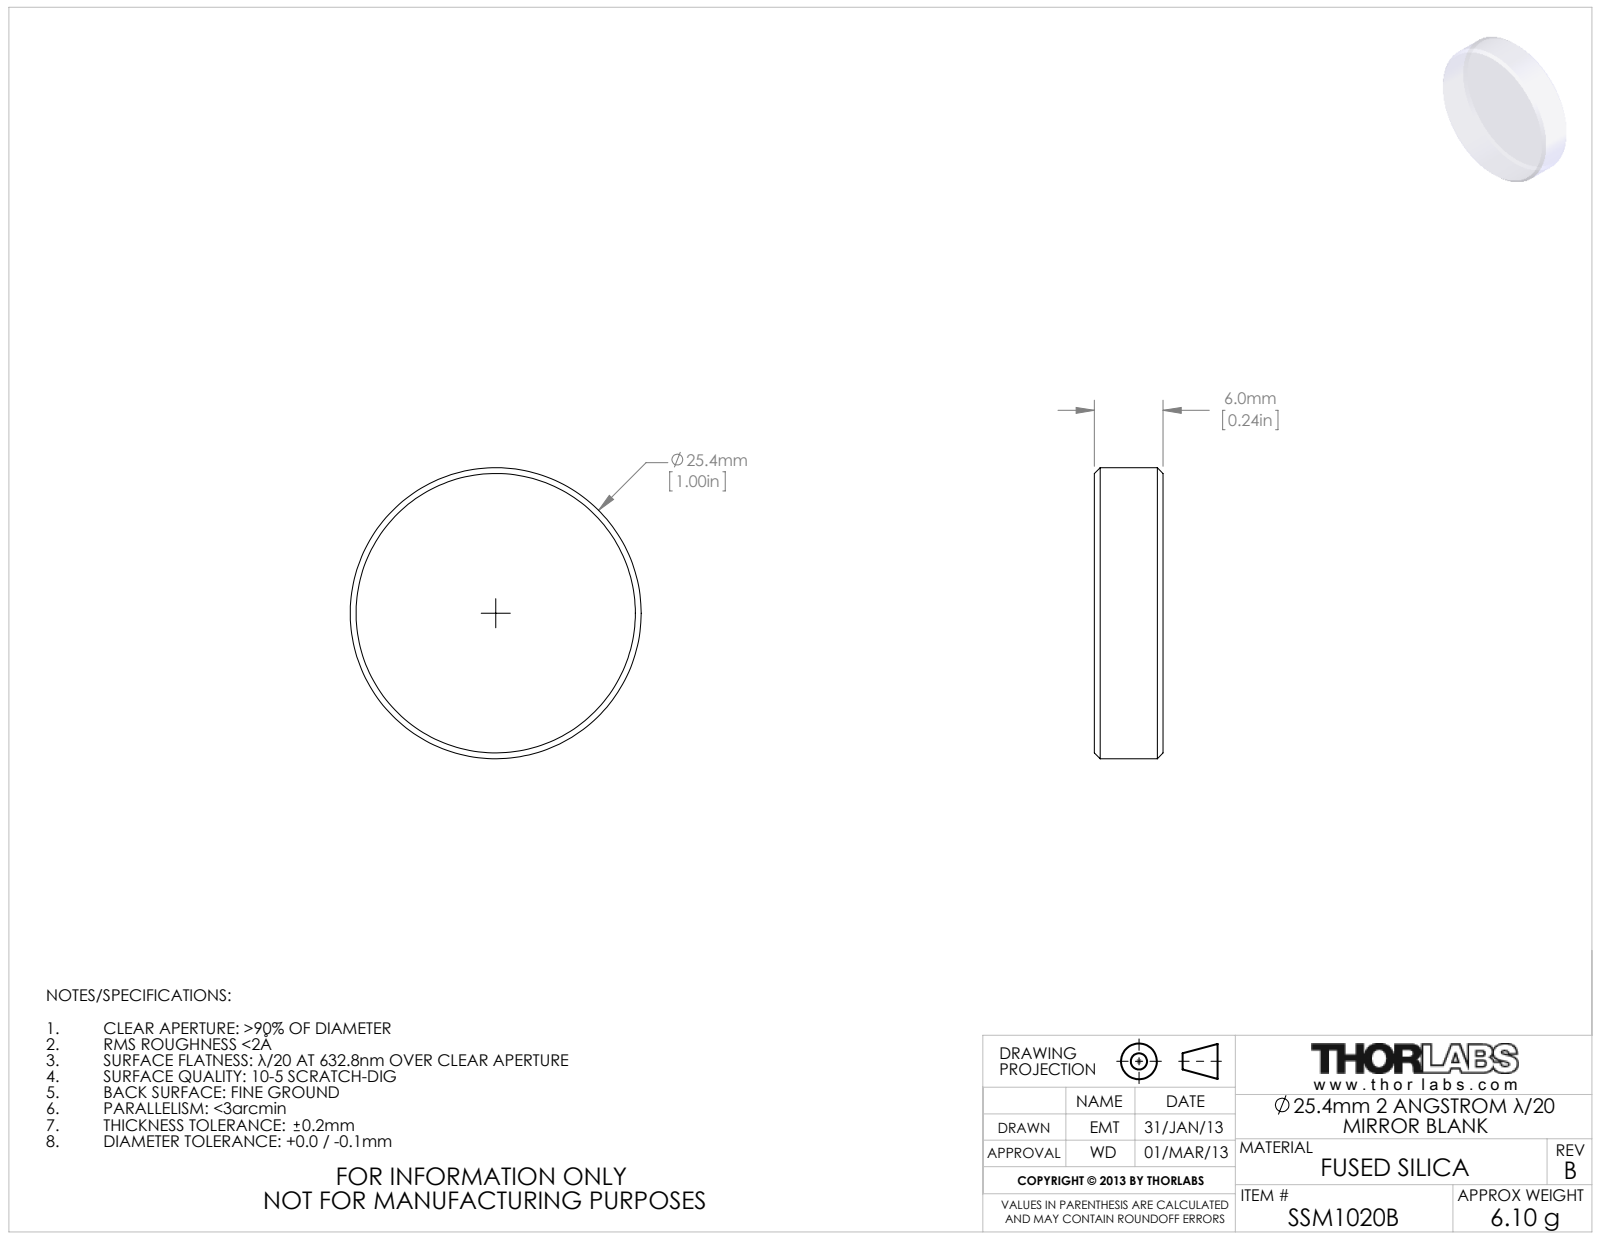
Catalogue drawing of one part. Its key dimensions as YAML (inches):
part_name: "TTN008870-E0W"
step_written_by: "SolidWorks 2012 (CONFIG_CONTROL_DESIGN)"
units: inches
bodies: {solids: 0, faces: 8, planar: 2, cylindrical: 2, other: 4}
overall_size: [1, 1, 0.236]
round_bosses_or_shafts:
  - {diameter: 1, count: 1}
face_to_face_distances: [0.236]
